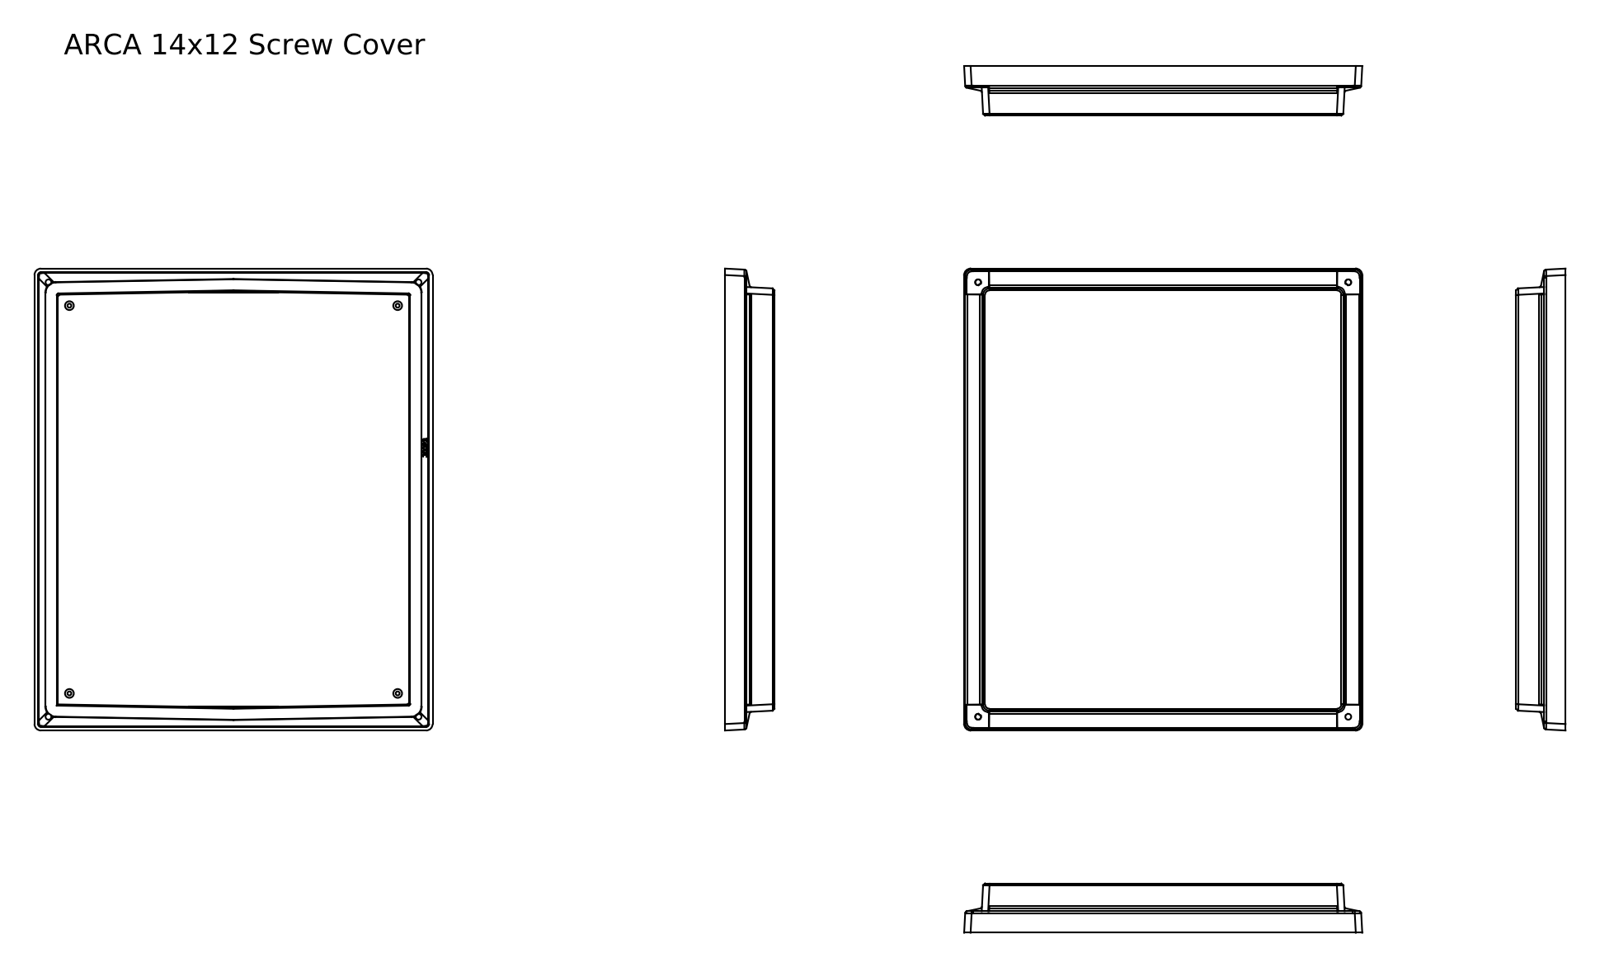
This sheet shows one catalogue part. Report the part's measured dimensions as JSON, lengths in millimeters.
{"part_name": "14x12_screw_cover", "step_written_by": "SolidWorks 2008 (AUTOMOTIVE_DESIGN)", "units": "millimeters", "bodies": {"solids": 1, "faces": 233, "planar": 88, "cylindrical": 66, "other": 79}, "overall_size": [393.34, 338.84, 42], "volume_mm3": 766908, "surface_area_mm2": 386694, "round_holes": [[3.4, 4], [5, 1]], "round_bosses_or_shafts": [[7.5, 4]], "partial_cylinders_radius": [[0.3, 8], [2, 8], [2.5, 7], [5.5, 4], [8.8, 4], [23, 4], [1.5, 3]], "face_to_face_distances": [3.6, 3, 30.4, 13.98, 34, 10.98, 14.73, 3.5, 11.73, 310.01], "hole_center_spacings": [279.4, 330.2, 432.55, 26.69, 297.88, 350.52, 459.23]}
